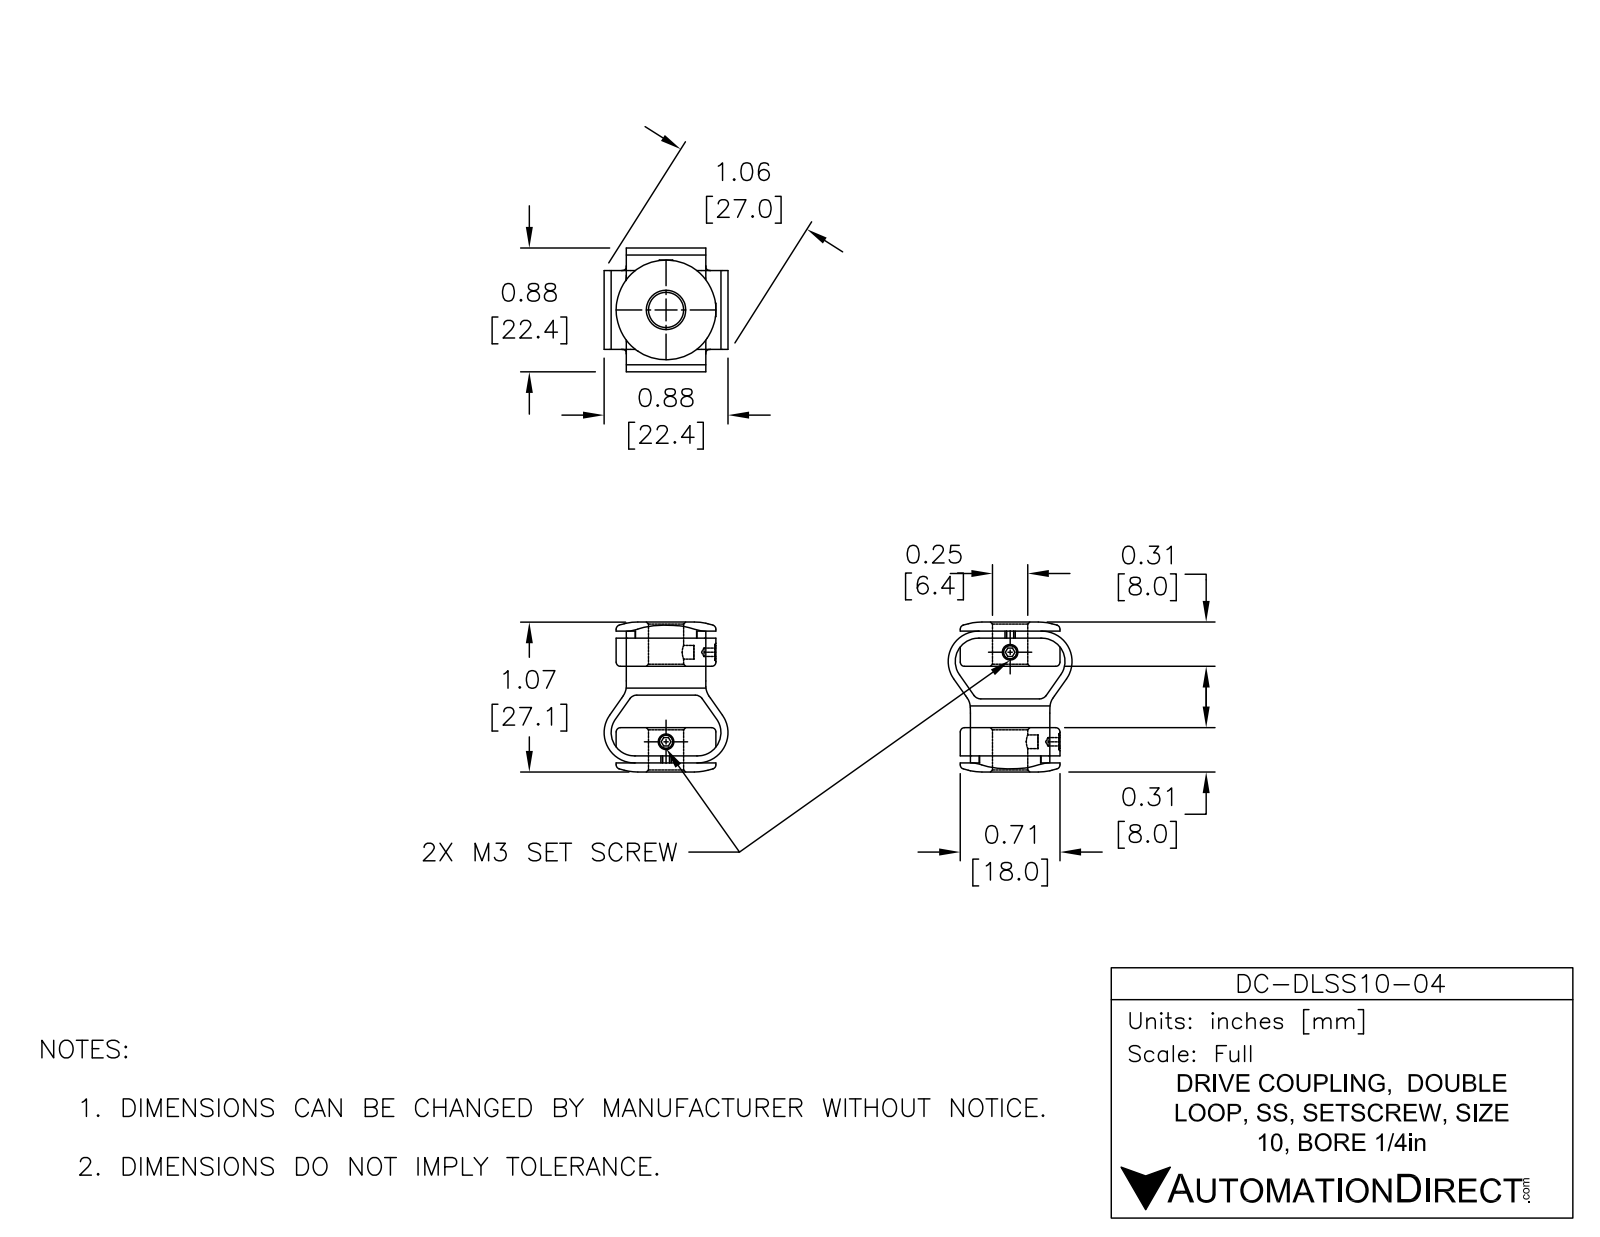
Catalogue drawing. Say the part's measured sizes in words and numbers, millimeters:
The part is named "DC-DLSS10-04". Its 3-D file was written by "SolidWorks 2015 (AUTOMOTIVE_DESIGN)". It is 1 solid with 110 faces: 57 planar, 28 cylindrical and 25 other. Overall it measures 33.4 by 22.35 by 22.35 millimeters. Its volume is 4 144 cubic millimeters and its surface area 3 961 square millimeters. Round holes: 1 of diameter 6.35. Round bosses or shafts: 1 of diameter 18.01. Partial cylindrical surfaces (rounded edges, fillets, slot ends): 4 of radius 4.19, 4 of radius 5.46, 1 of radius 5.59. The main face-to-face distances are 1.27, 33.4, 16.38, 17.02, 17.65, 15.75, 7.06, 26.34, 12.23, 11.6.
